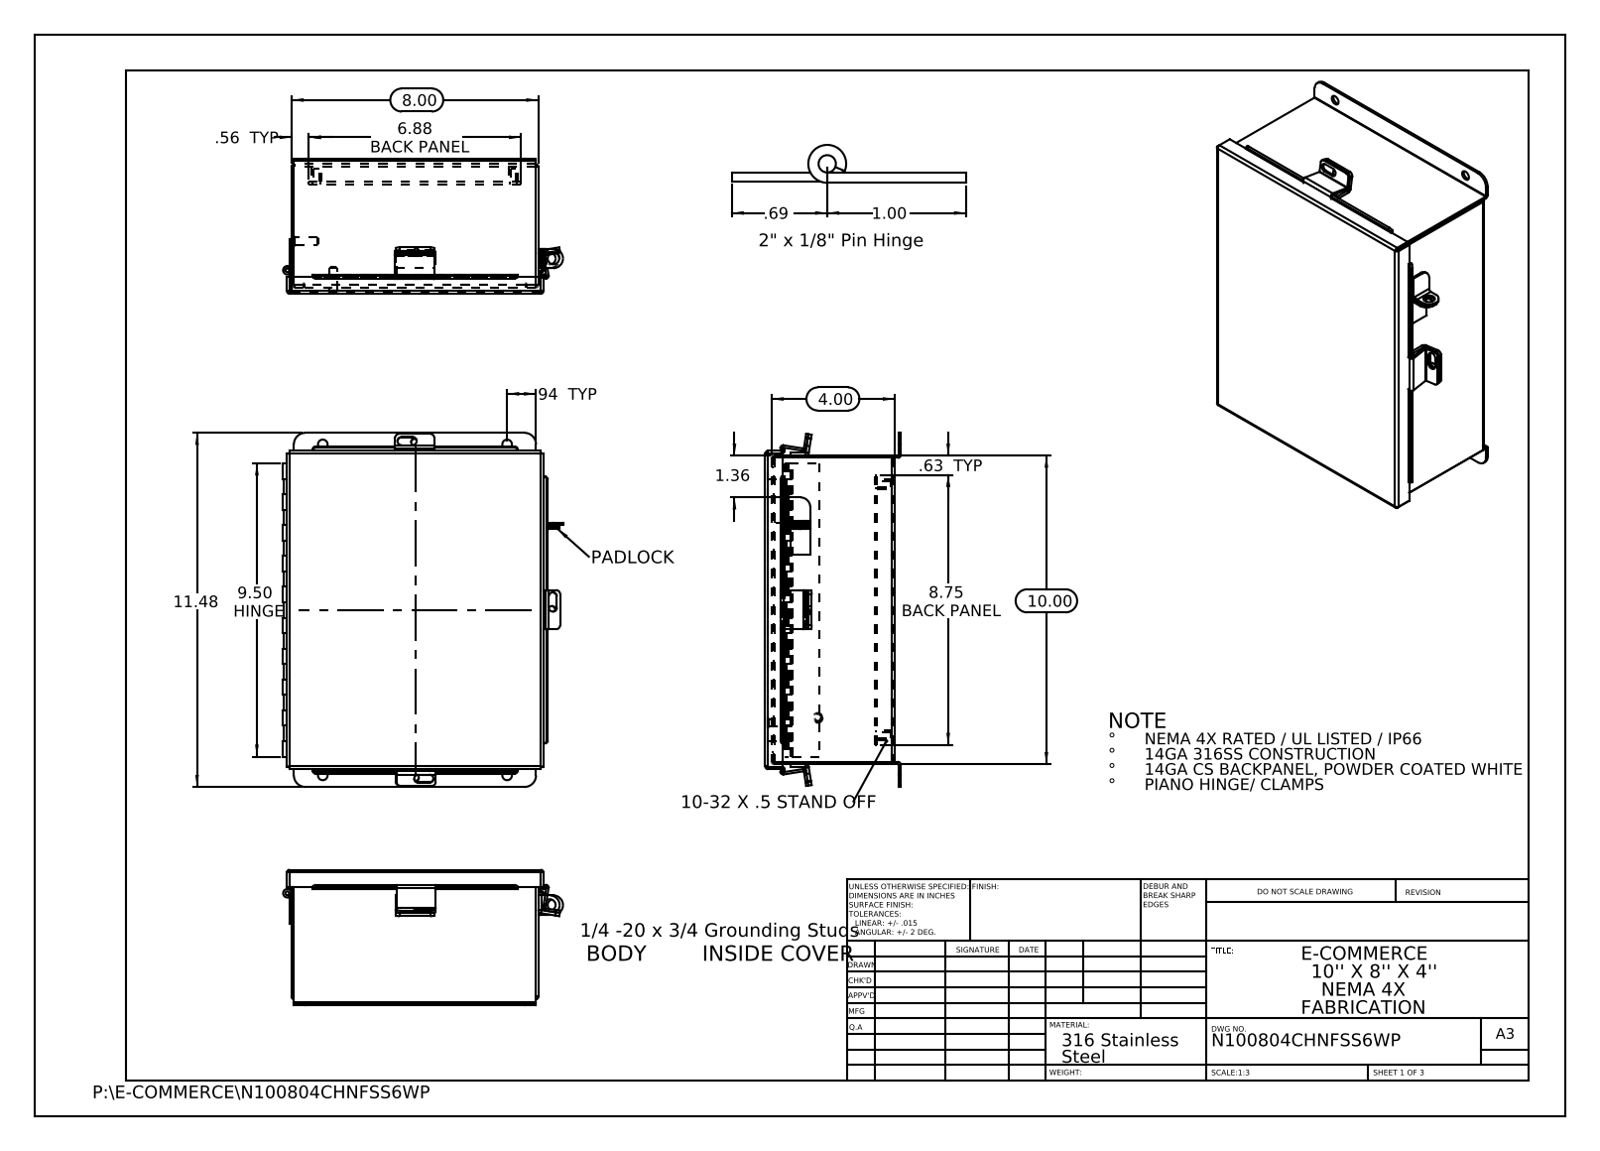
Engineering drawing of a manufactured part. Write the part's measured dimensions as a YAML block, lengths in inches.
part_name: "N100804CHNFSS6WP JIC Enclosure Template; N100804CHNFSS6WP Hinge Body Side; N100804CHNFSS6WP Hinge Cover Side JIC; N100804CHNFSS6WP _JIC Hinge (+8 more)"
step_written_by: "SolidWorks 2013 (CONFIG_CONTROL_DESIGN)"
units: inches
bodies: {solids: 21, faces: 620, planar: 383, cylindrical: 217, other: 20}
overall_size: [11.476, 9.072, 4.39]
volume: 32.93
surface_area: 904.4
round_holes:
  - {diameter: 0.25, count: 7}
  - {diameter: 0.187, count: 4}
  - {diameter: 0.312, count: 4}
  - {diameter: 0.125, count: 1}
  - {diameter: 0.373, count: 1}
  - {diameter: 0.375, count: 1}
round_bosses_or_shafts:
  - {diameter: 0.313, count: 4}
  - {diameter: 0.315, count: 2}
  - {diameter: 0.236, count: 2}
  - {diameter: 0.273, count: 1}
  - {diameter: 0.25, count: 1}
partial_cylinders:
  - {radius: 0.013, count: 13}
  - {radius: 0.009, count: 12}
  - {radius: 0.088, count: 12}
  - {radius: 0.125, count: 10}
  - {radius: 0.083, count: 6}
  - {radius: 0.1, count: 6}
  - {radius: 0.133, count: 6}
  - {radius: 0.375, count: 4}
face_to_face_distances: [0.075, 4.128, 4.053, 4.203, 7.925, 9.925, 0.074, 0.575, 0.5, 3.553]
hole_center_spacings: [1.315, 6.311, 9.428, 11.269, 5.976, 6.375, 8.126, 10.328]
